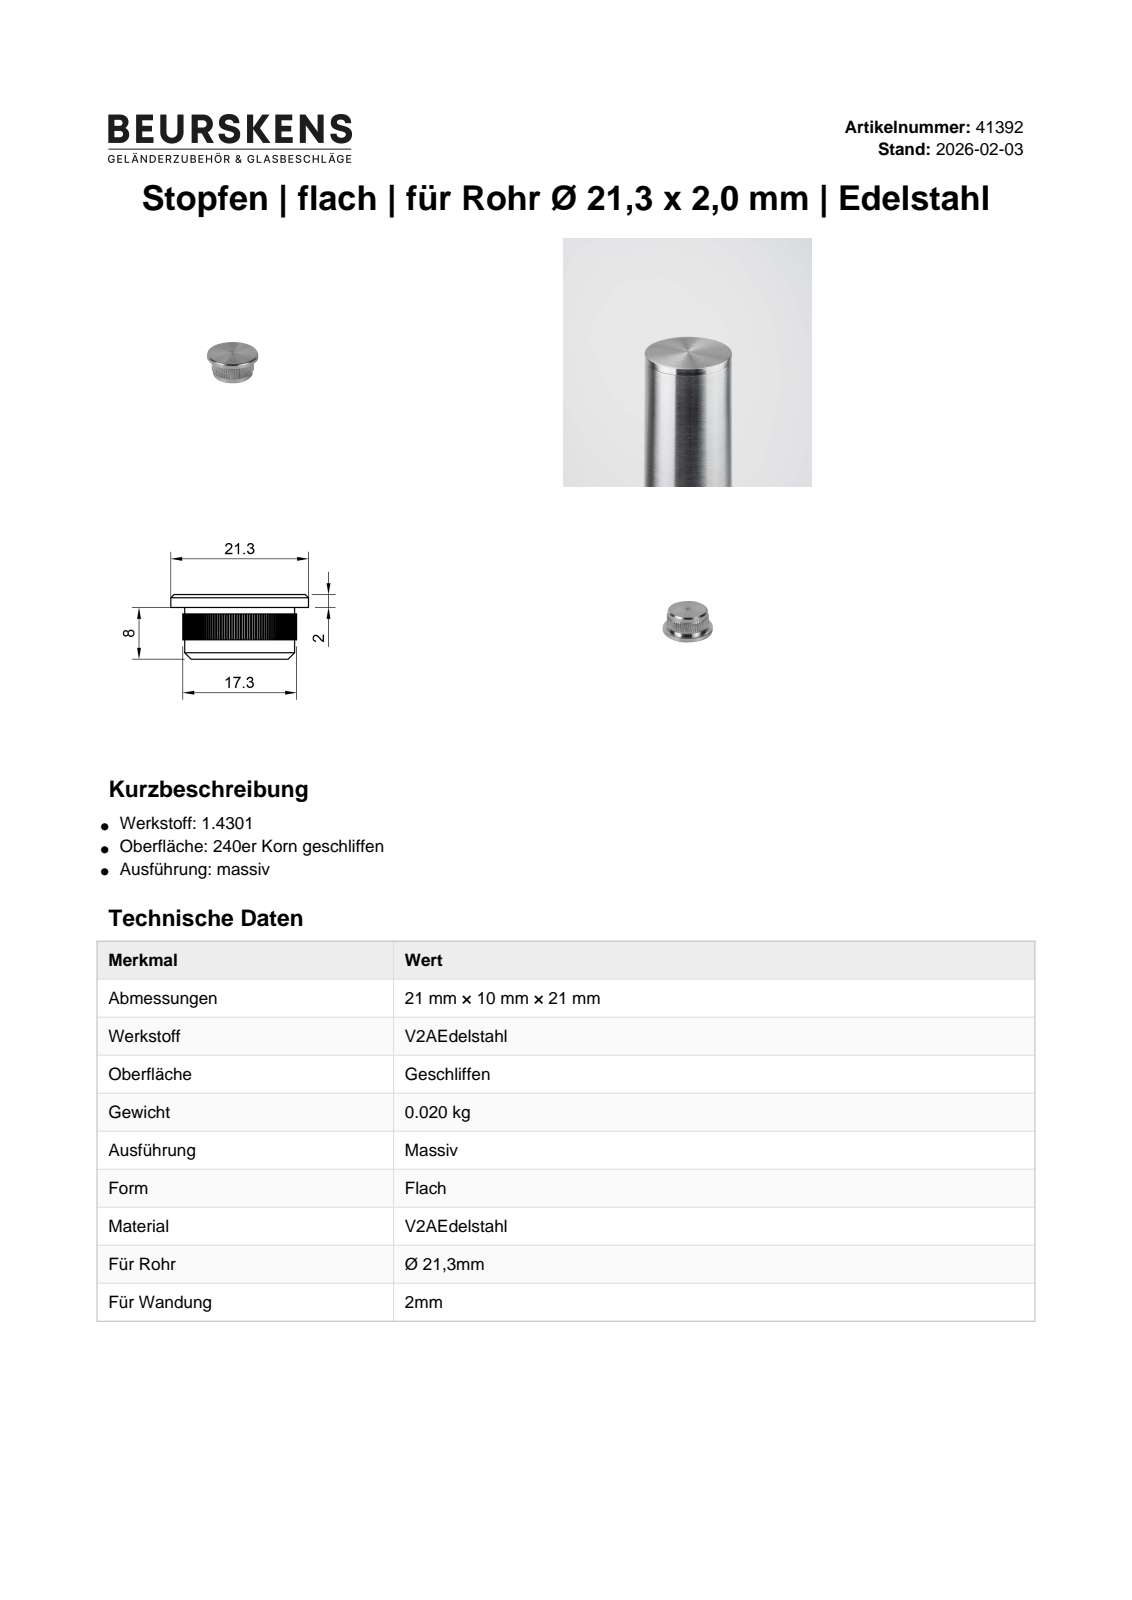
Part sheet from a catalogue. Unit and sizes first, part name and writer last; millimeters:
Units: millimetres
Overall size (bounding box): 21.3 × 21.3 × 10
Round bosses / shafts (diameter × count): ⌀21.3 ×1, ⌀17 ×1
Partial cylindrical surfaces — rounded edges, fillets, slot ends (radius × count): R0.12 ×140, R8.8 ×1
Main face-to-face distances: 10, 8, 2, 3, 7, 1, 4, 5
Volume: 2 546 mm³ · Surface area: 1 333 mm²
Bodies: 1 solid, 290 faces (5 planar, 283 cylindrical, 2 other)
Part name (STEP PRODUCT): 41392
STEP written by: Autodesk Inventor 2022 (AUTOMOTIVE_DESIGN)
